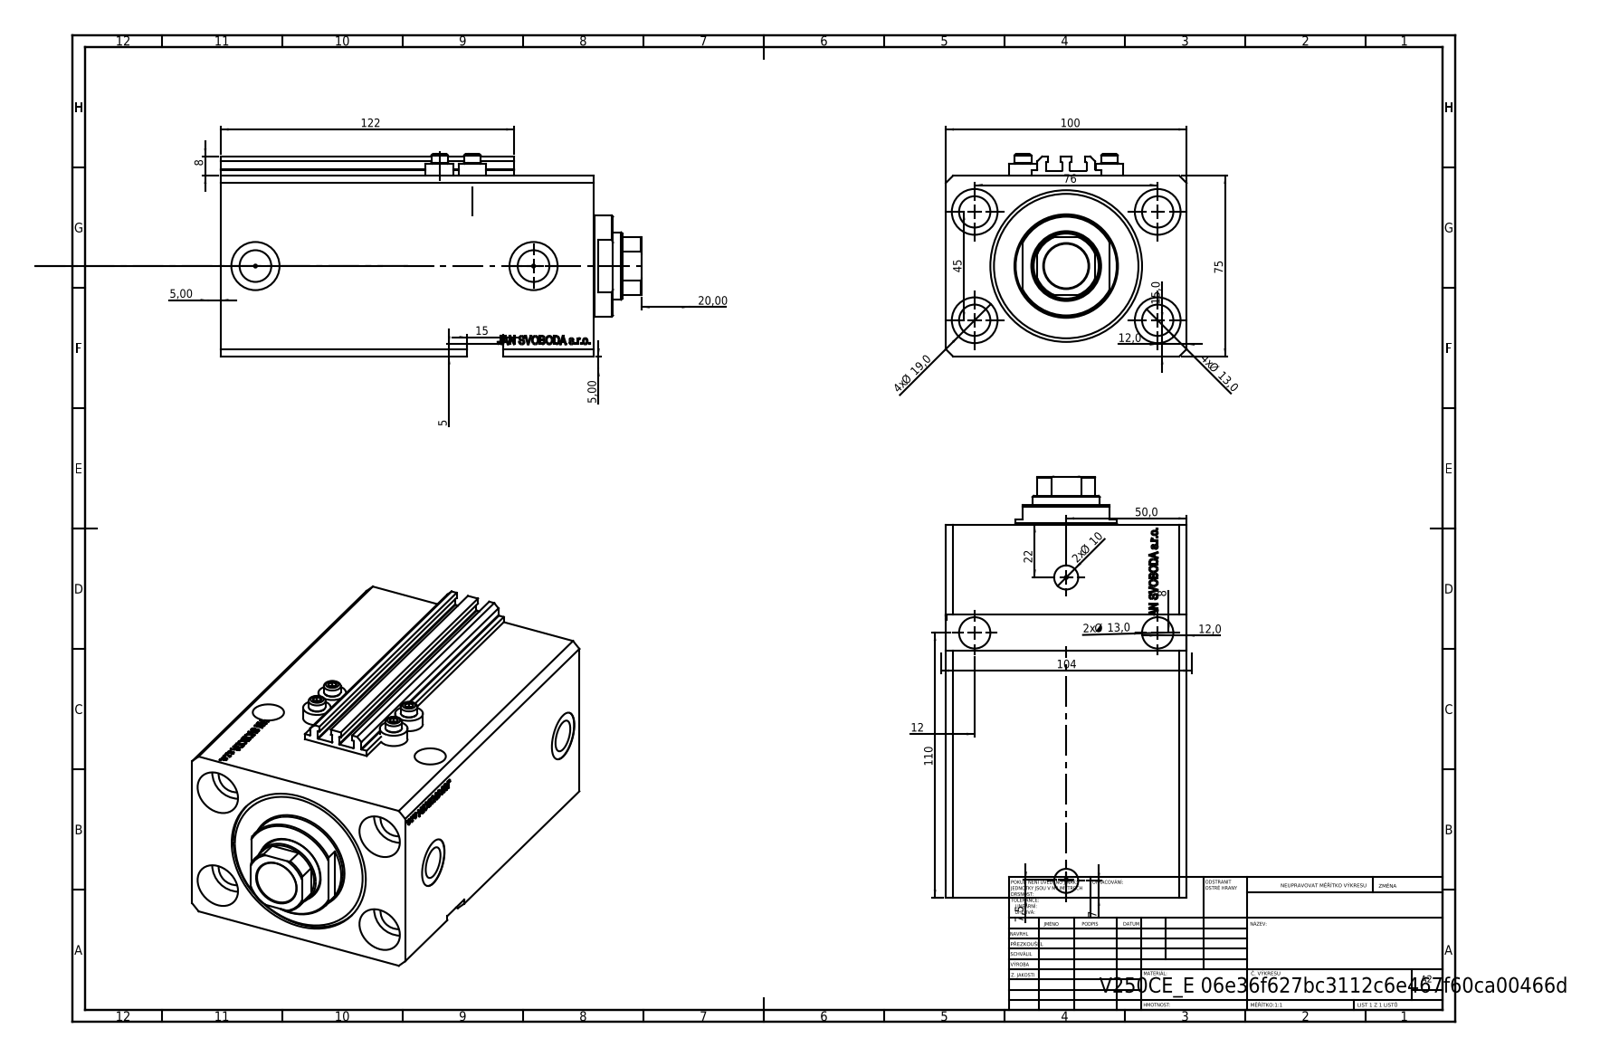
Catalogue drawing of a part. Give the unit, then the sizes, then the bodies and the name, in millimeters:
Units: millimetres
Overall size (bounding box): 174.9 × 100 × 84
Round holes (diameter × count): ⌀13 ×6, ⌀1.25 ×4, ⌀4 ×4, ⌀19 ×4, ⌀10 ×2, ⌀13.16 ×2, ⌀20 ×2, ⌀18.5 ×1, ⌀28 ×1, ⌀50 ×1, ⌀63 ×1
Round bosses / shafts (diameter × count): ⌀11.6 ×4, ⌀7 ×4, ⌀42 ×1
Partial cylindrical surfaces — rounded edges, fillets, slot ends (radius × count): R0.2 ×10, R13.5 ×1
Main face-to-face distances: 75, 100, 155, 11.9, 143.1, 128.4, 116.5, 26.6, 48.4, 8
Hole centre spacings: 44.16, 76, 13.6, 20.72, 27.59, 33.62, 36, 38.48
Volume: 951 083 mm³ · Surface area: 175 815 mm²
Bodies: 8 solids, 1104 faces (539 planar, 138 cylindrical, 427 other)
Part name (STEP PRODUCT): V250CE_C_VCP; V250CE_VC_E; V250CE_E_Body; ALLEN BOLT V250CE
STEP written by: SolidWorks 2019 (CONFIG_CONTROL_DESIGN)
